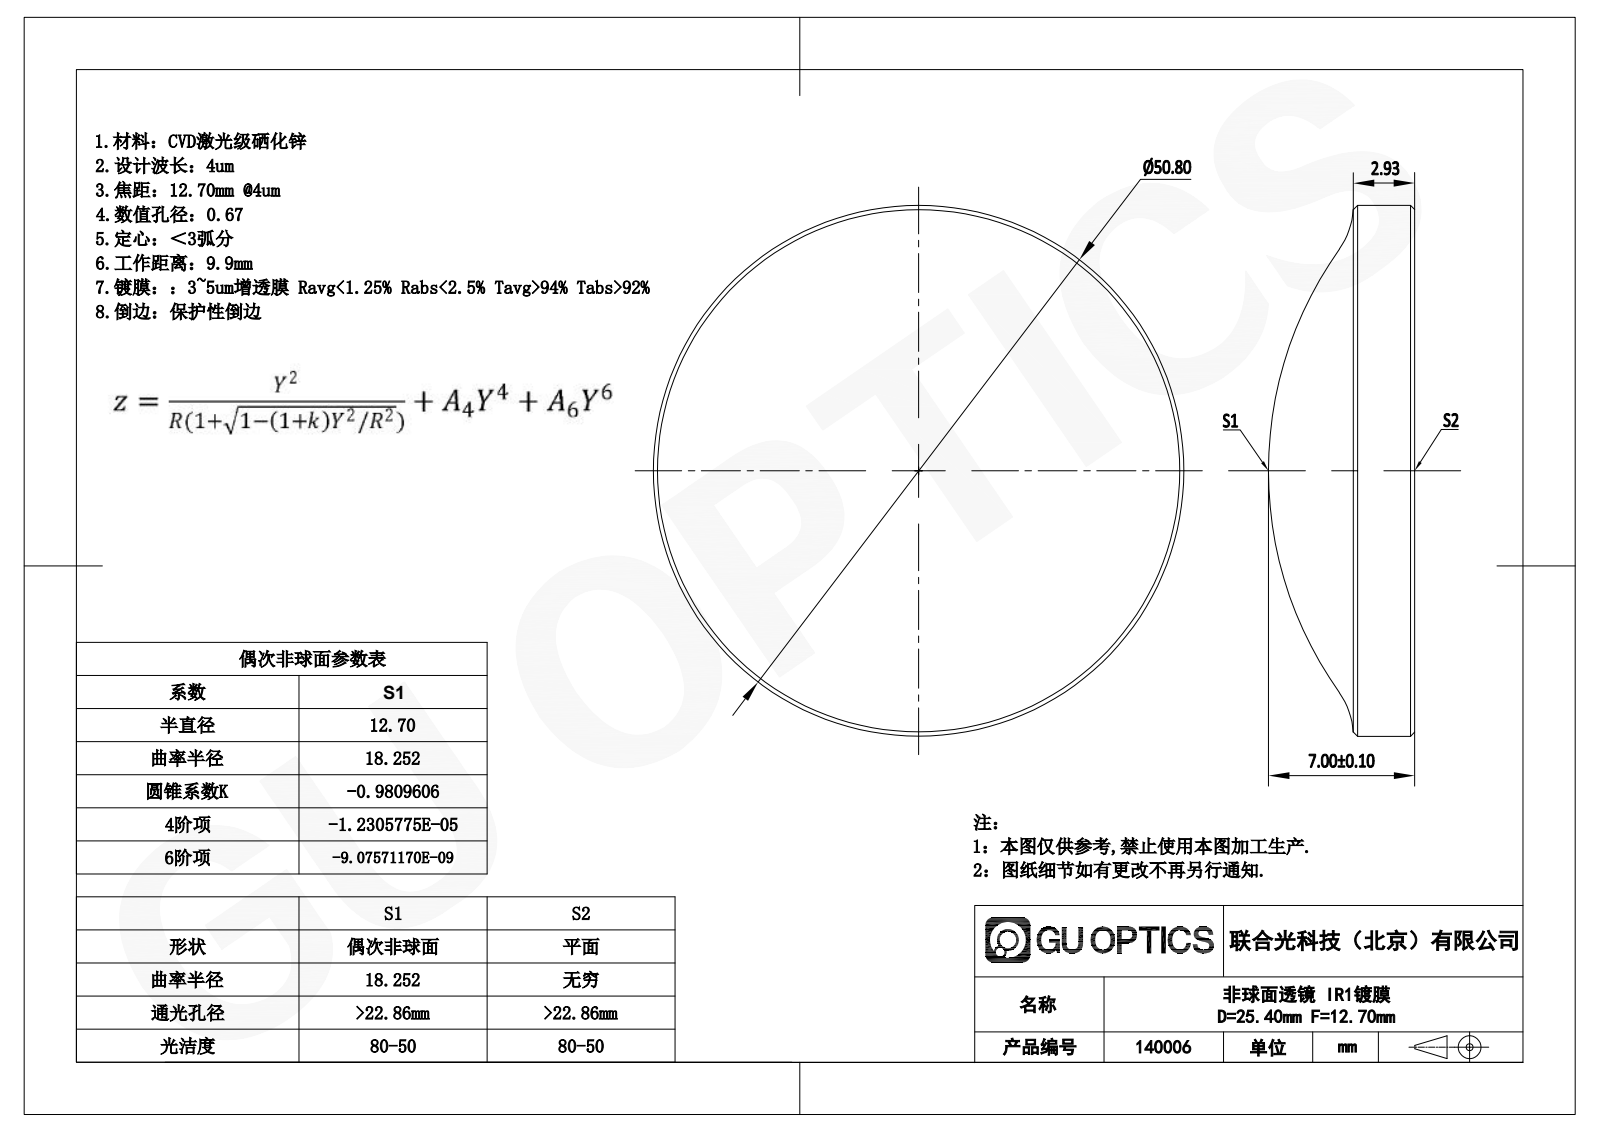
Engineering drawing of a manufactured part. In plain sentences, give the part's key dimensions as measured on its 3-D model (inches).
The part is named "GL7AL1-025-012-IR1". Its 3-D file was written by "SolidWorks 2022 (AUTOMOTIVE_DESIGN)". It is 1 solid with 11 faces: 1 planar, 2 cylindrical and 8 other. Overall it measures 1 by 1 by 0.276 inches. Its volume is 0.145 cubic inches and its surface area 1.976 square inches. Round bosses or shafts: 1 of diameter 1.
